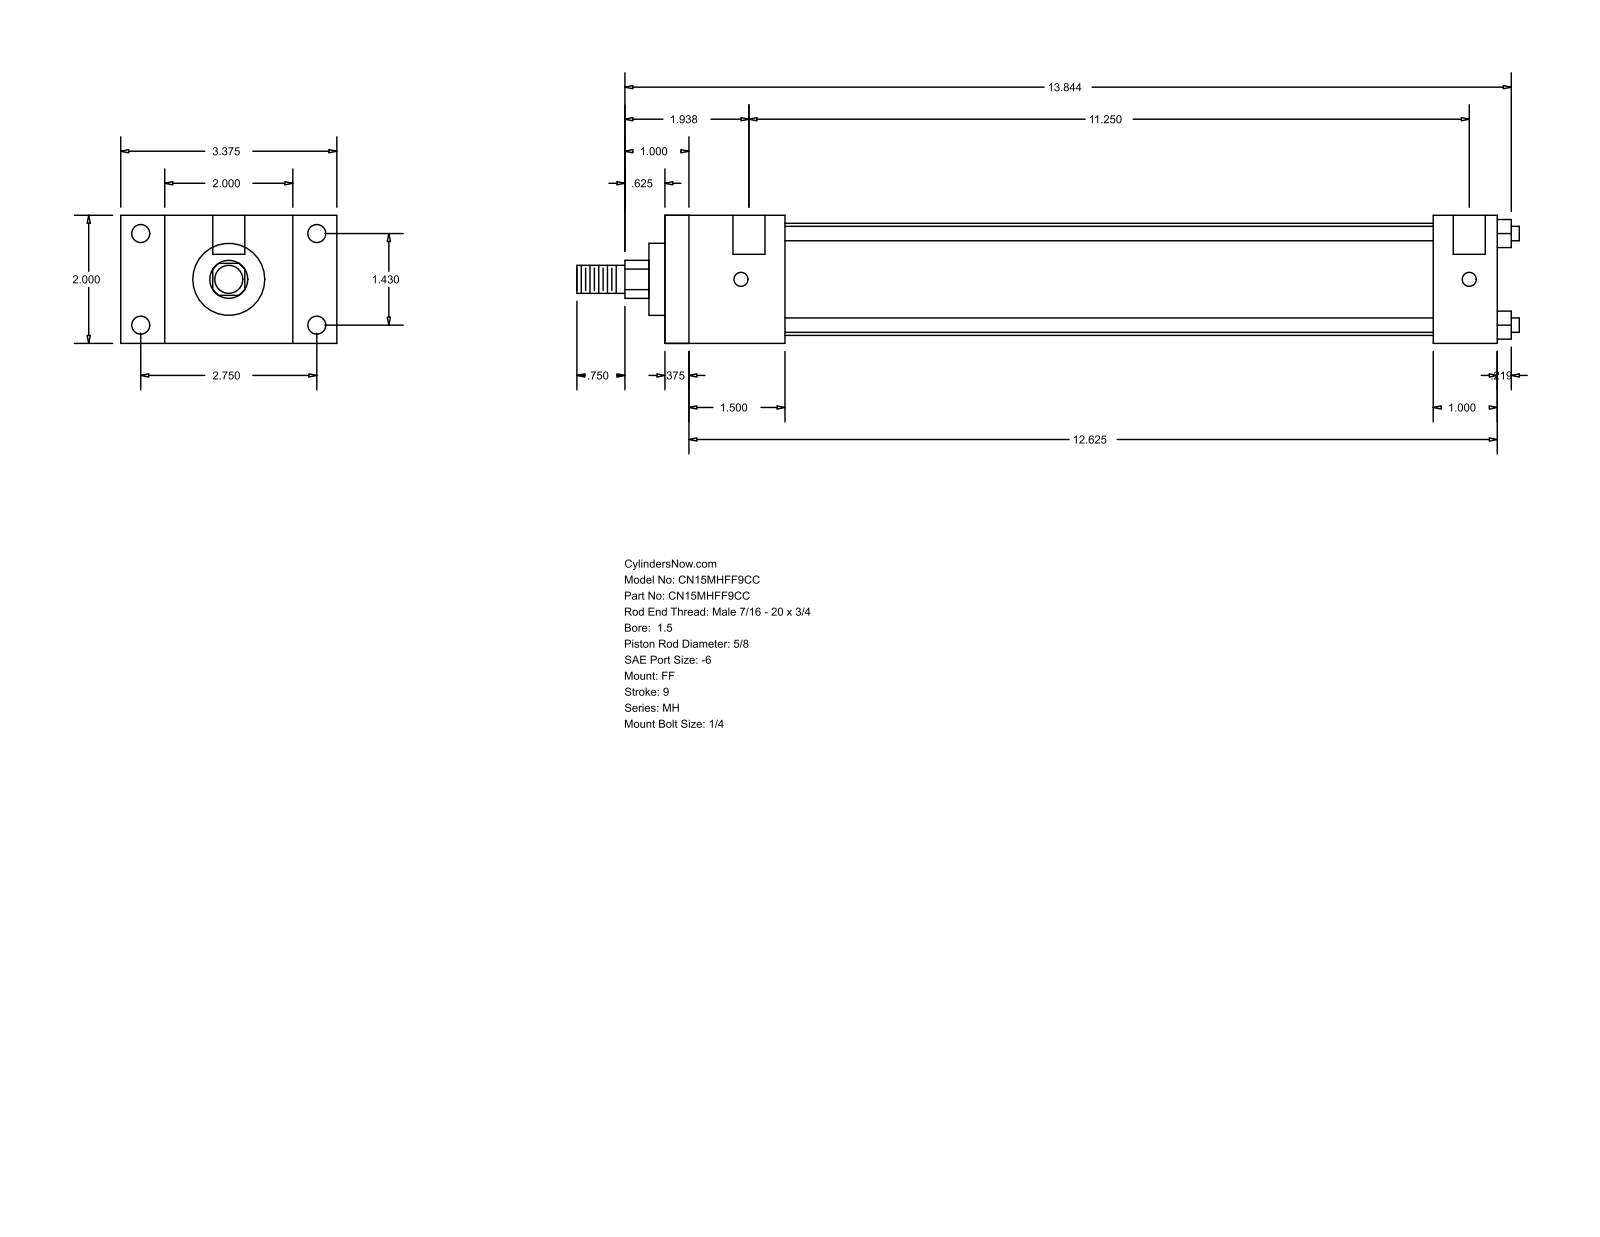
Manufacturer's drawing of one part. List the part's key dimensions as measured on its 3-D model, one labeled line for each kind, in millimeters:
Part name (STEP PRODUCT): MH_FF__0150_0.625
STEP written by: GSSL Pune (CONFIG_CONTROL_DESIGN)
Units: millimetres
Bodies: 0 solids, 92 faces (64 planar, 28 cylindrical, 0 other)
Overall size (bounding box): 373.86 × 85.72 × 50.8
Round holes (diameter × count): ⌀5.56 ×4, ⌀7.14 ×4, ⌀12.7 ×2
Round bosses / shafts (diameter × count): ⌀5.71 ×4, ⌀44.45 ×1, ⌀28.57 ×1, ⌀15.88 ×1, ⌀11.11 ×1
Partial cylindrical surfaces — rounded edges, fillets, slot ends (radius × count): R7.54 ×1
Main face-to-face distances: 50.8, 330.19, 9.52, 320.67, 17.46, 68.26, 47.62, 38.1, 282.57, 304.8
Hole centre spacings: 36.32, 69.84, 78.72, 288.92, 3.17, 285.75
